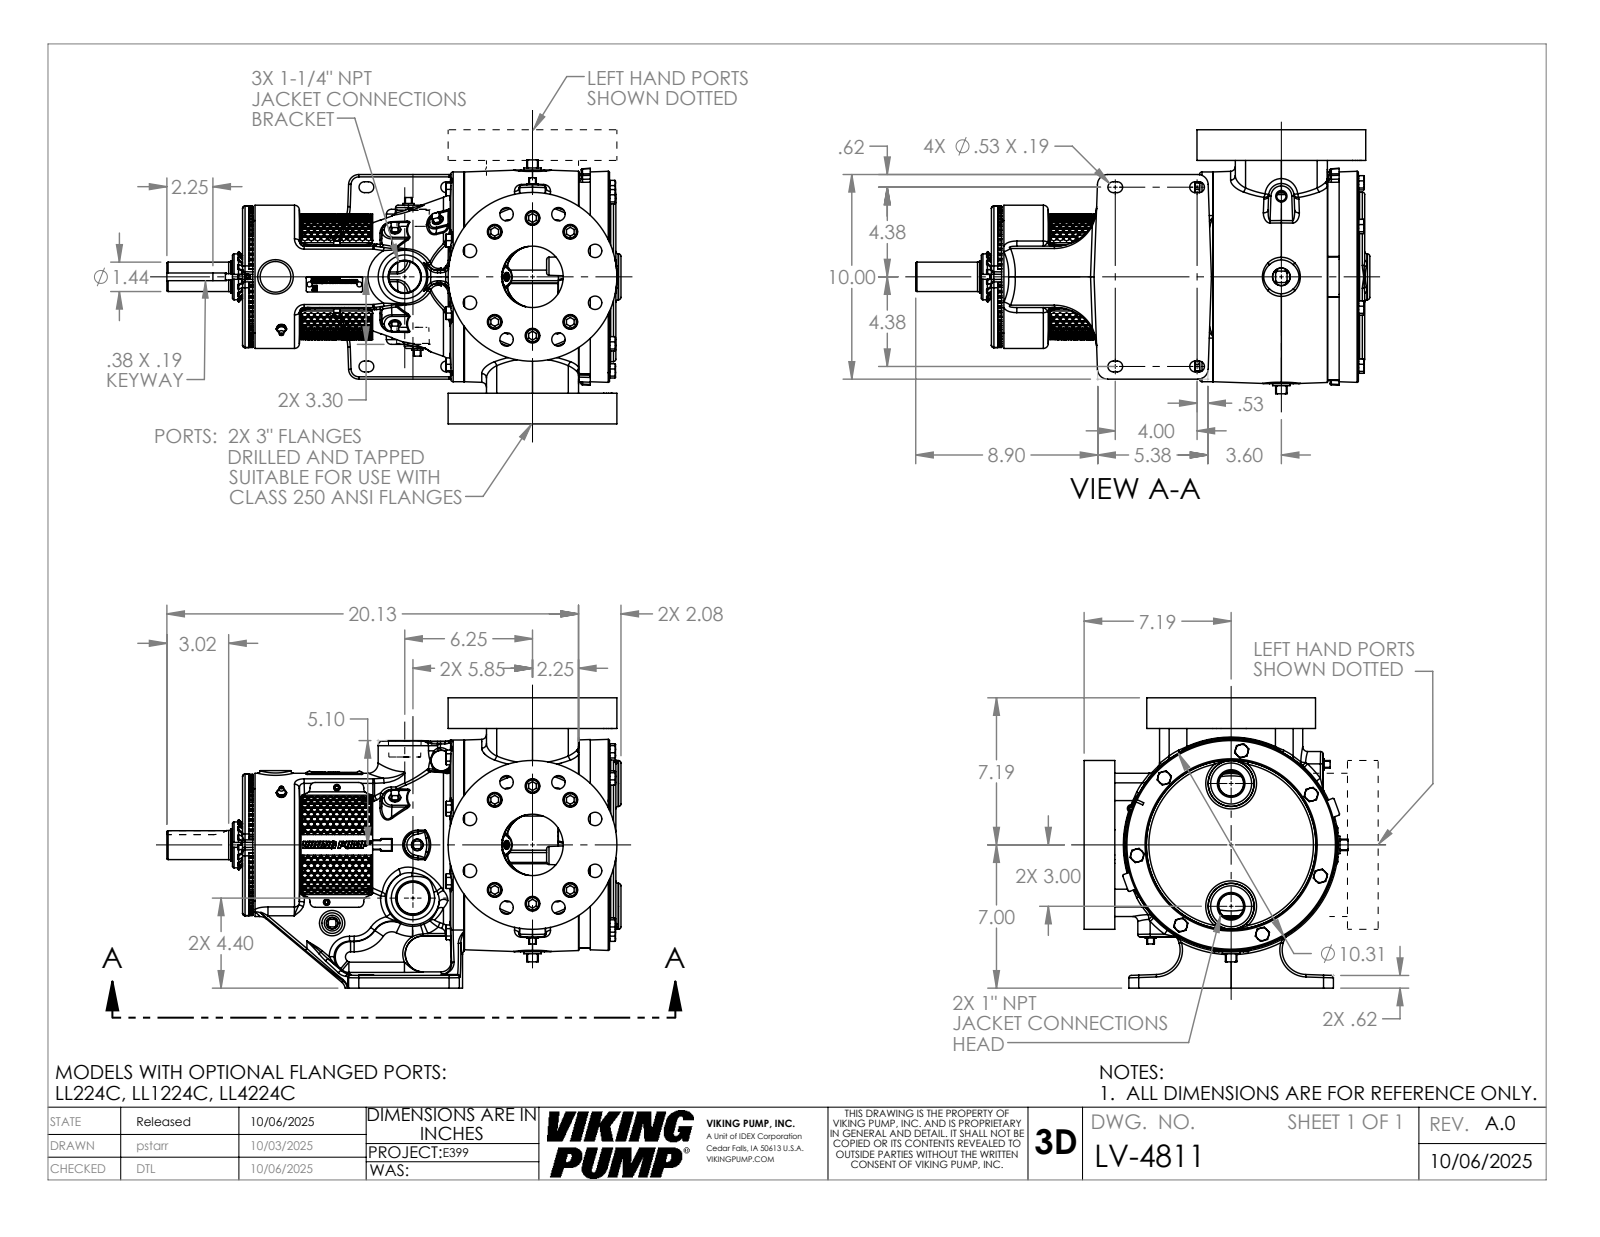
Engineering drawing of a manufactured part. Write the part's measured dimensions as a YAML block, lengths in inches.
part_name: "LV-4811"
step_written_by: "SolidWorks 2024 (AUTOMOTIVE_DESIGN)"
units: inches
bodies: {solids: 1, faces: 4472, planar: 1501, cylindrical: 868, other: 2103}
overall_size: [22.2, 14.188, 12.903]
volume: 1208
surface_area: 1492
round_holes:
  - {diameter: 0.656, count: 16}
  - {diameter: 0.719, count: 12}
  - {diameter: 0.25, count: 9}
  - {diameter: 0.368, count: 8}
  - {diameter: 1.094, count: 8}
  - {diameter: 0.199, count: 6}
  - {diameter: 0.159, count: 3}
  - {diameter: 0.266, count: 2}
  - {diameter: 0.313, count: 2}
  - {diameter: 3, count: 2}
  - {diameter: 0.453, count: 1}
  - {diameter: 1.577, count: 1}
round_bosses_or_shafts:
  - {diameter: 0.66, count: 12}
  - {diameter: 0.625, count: 8}
  - {diameter: 0.625, count: 7}
  - {diameter: 0.312, count: 3}
  - {diameter: 0.19, count: 3}
  - {diameter: 8.25, count: 2}
  - {diameter: 10.25, count: 1}
  - {diameter: 7, count: 1}
partial_cylinders:
  - {radius: 0.063, count: 109}
  - {radius: 0.069, count: 74}
  - {radius: 0.12, count: 58}
  - {radius: 0.5, count: 26}
  - {radius: 0.03, count: 18}
  - {radius: 0.24, count: 16}
  - {radius: 0.06, count: 13}
  - {radius: 0.25, count: 12}
face_to_face_distances: [1.5, 14.187, 12.687, 0.31, 2.25, 0.5, 11.65, 11.96, 3.54, 15.19]
hole_center_spacings: [2.875, 3.313, 4.685, 3, 2.535, 1.375, 0.458, 0.75]
